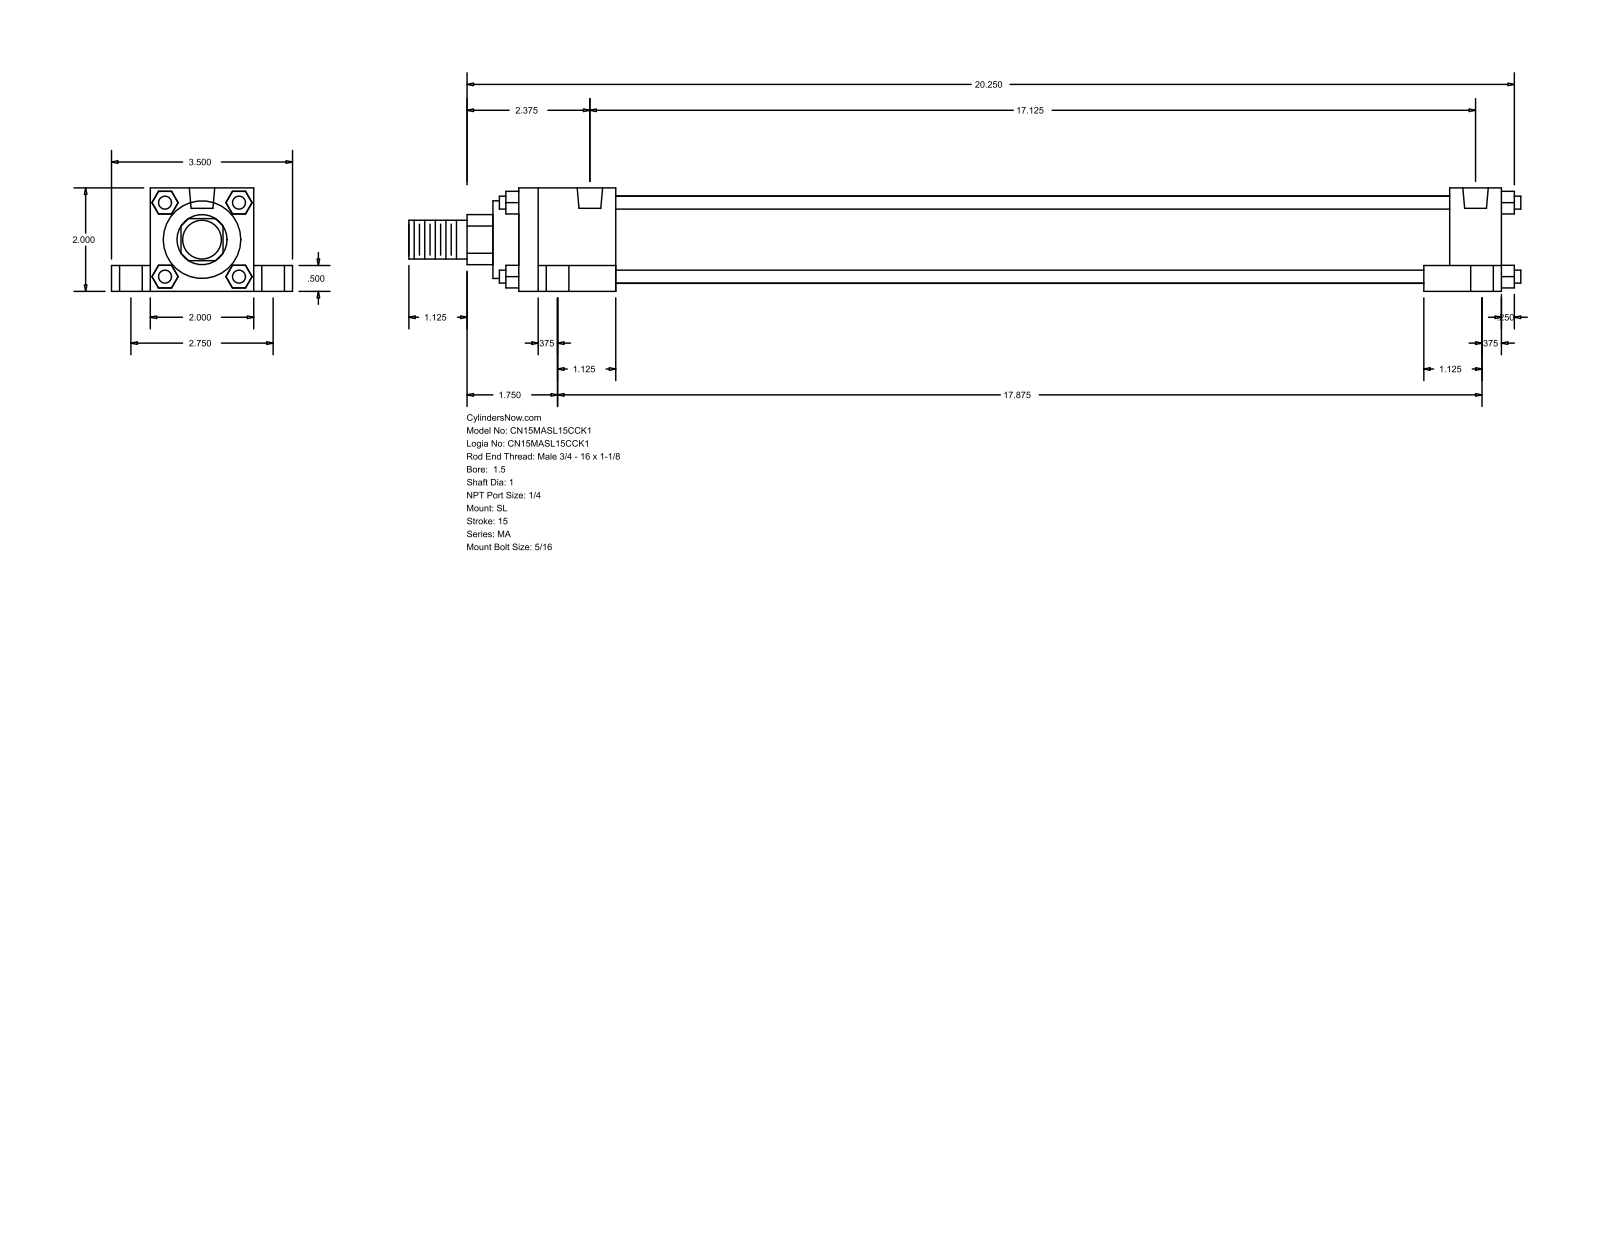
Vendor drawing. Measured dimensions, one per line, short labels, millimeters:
name: MA_SL__0150_1
written by: GSSL Pune (CONFIG_CONTROL_DESIGN)
unit: mm
bodies: 0 solids, 148 faces (112 planar, 36 cylindrical, 0 other)
size: 546.1 × 88.9 × 50.8
holes: 4× ⌀7.94, 4× ⌀11.11, 4× ⌀17.46, 2× ⌀12.49
bosses: 4× ⌀6.35, 1× ⌀42.93, 1× ⌀38.1, 1× ⌀25.4, 1× ⌀19.05
rounds: 1× R12.29
face distances: 50.8, 12.7, 19.05, 69.85, 38.1, 9.52, 482.6, 25.4, 6.35, 457.2
hole spacings: 35.06, 38.36, 69.84, 434.97, 439.54, 452.2, 454.03, 459.37
